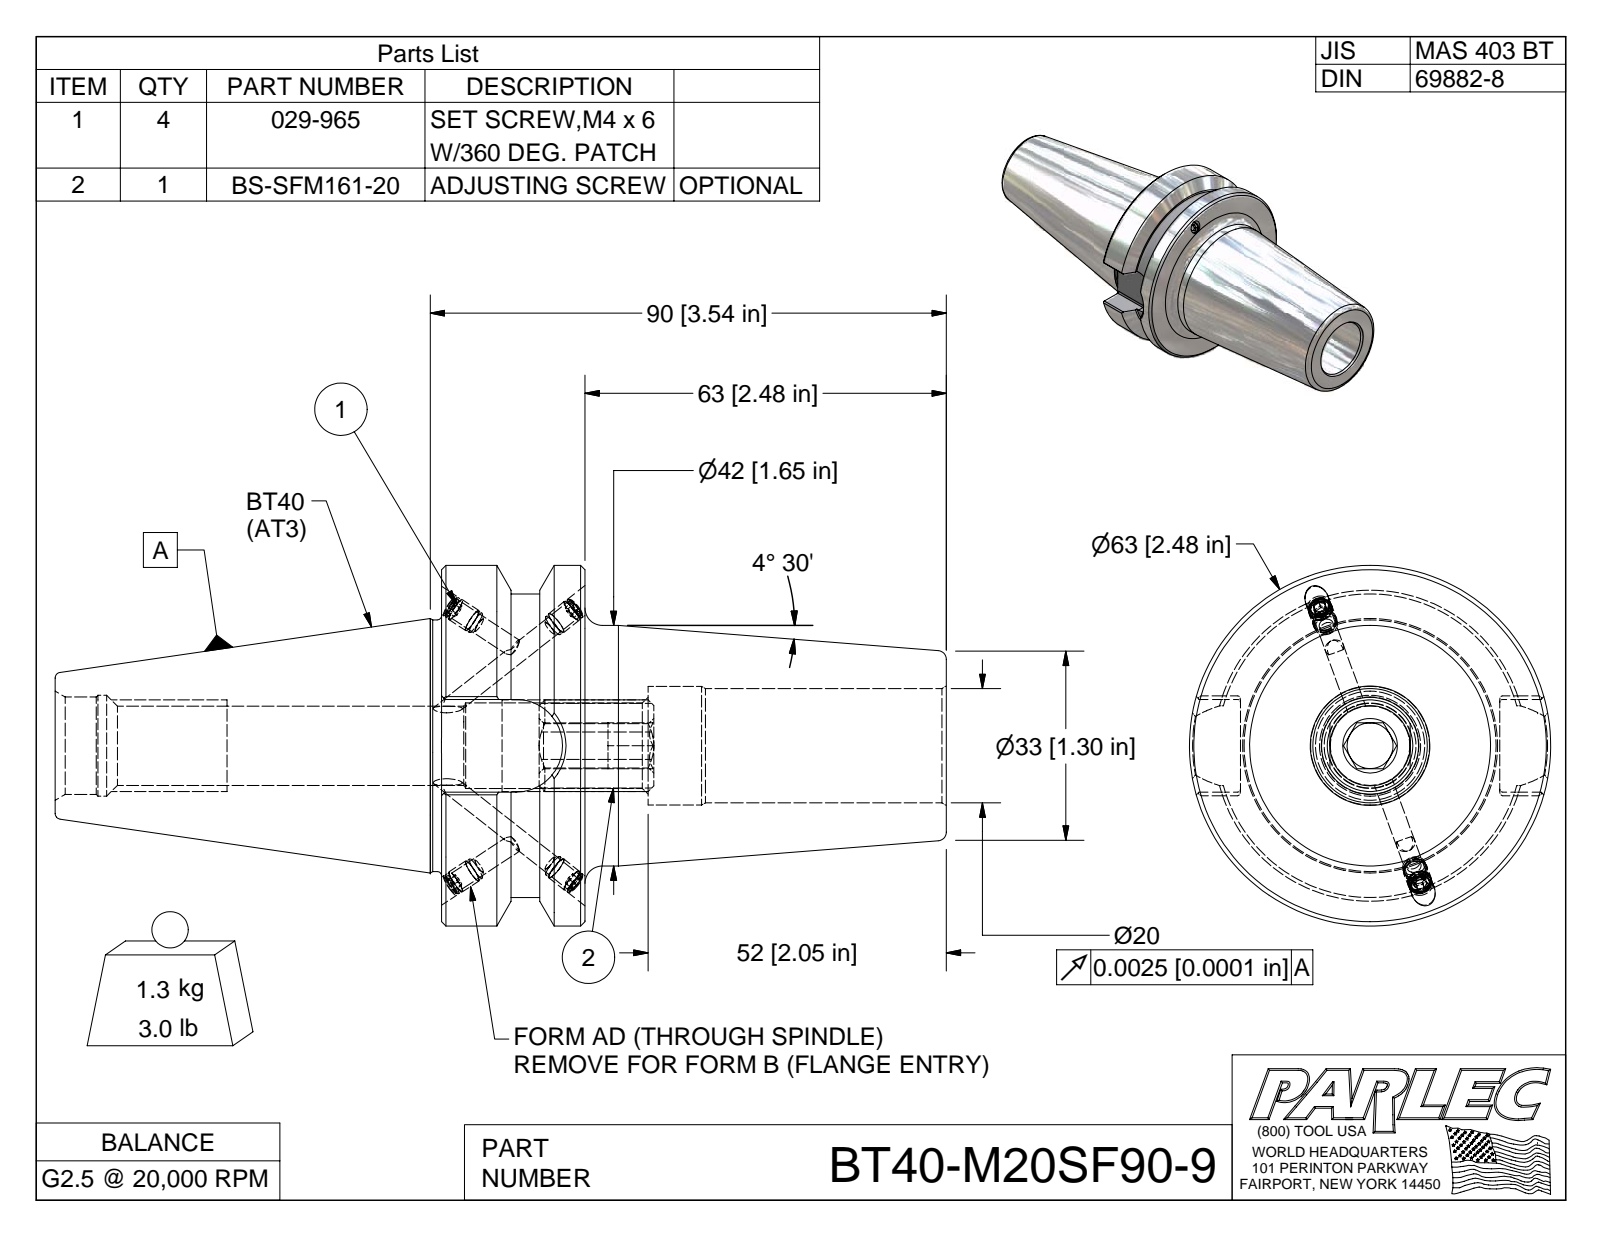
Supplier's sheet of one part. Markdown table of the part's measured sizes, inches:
| quantity | value |
| --- | --- |
| part name | BT40-M20SF90-9; BT40BC-M20SF90-9-1; 029-965; BS-SFM161-20 |
| STEP written by | Autodesk Inventor 2009 (AUTOMOTIVE_DESIGN) |
| units | inches |
| bodies | 6 solids, 173 faces (79 planar, 43 cylindrical, 51 other) |
| overall size | 6.118 × 2.48 × 2.48 |
| volume | 10.64 in³ |
| surface area | 55.74 in² |
| round holes (diameter × count) | 0.13 × 4, 0.161 × 4, 0.694 × 1, 0.786 × 1, 0.816 × 1 |
| round bosses / shafts (diameter × count) | 0.165 × 4, 0.157 × 4, 2.48 × 1, 2.087 × 1, 1.75 × 1, 1.73 × 1, 1.654 × 1 |
| partial cylindrical surfaces (radius × count) | 0.02 × 8, 0.315 × 1, 0.319 × 1 |
| main face-to-face distances | 0.984, 3.465, 2.481, 0.615, 1.166, 1.78, 2.653, 3.637, 6.119, 0.551 |
